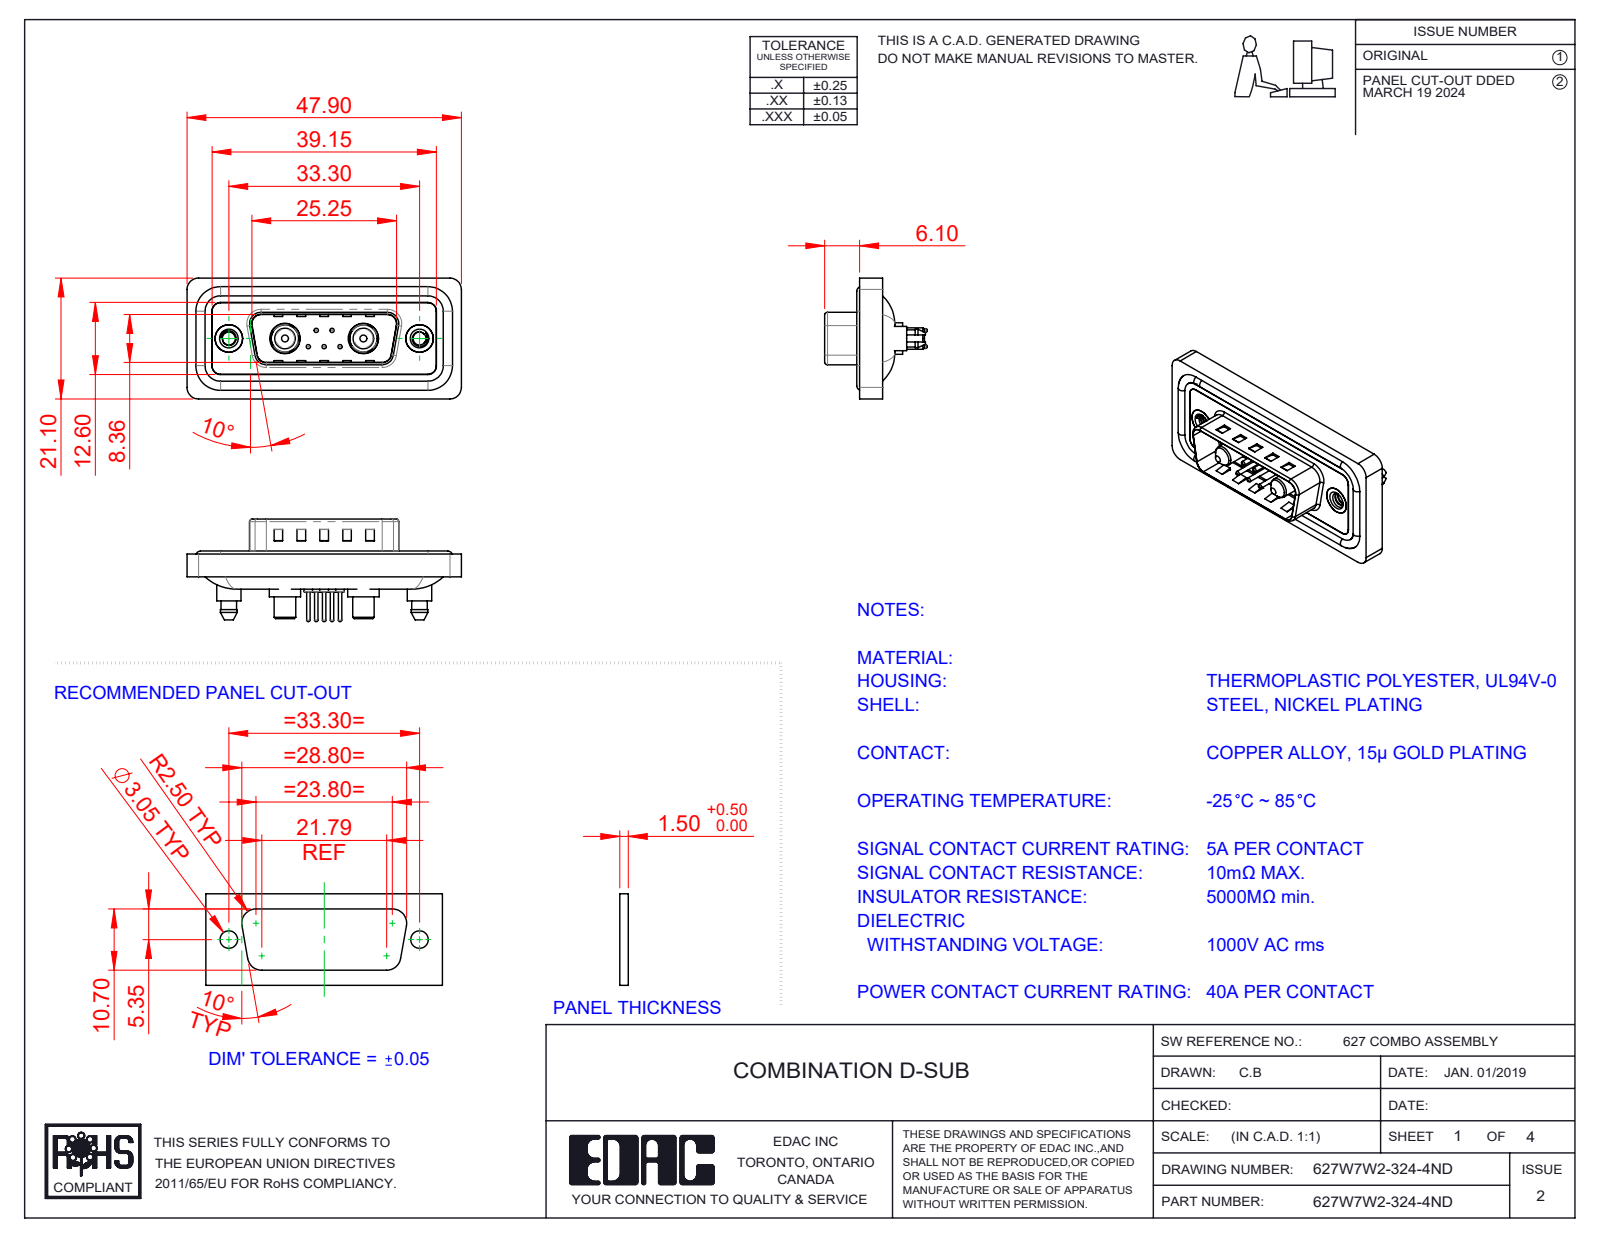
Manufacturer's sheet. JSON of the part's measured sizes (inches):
{"part_name": "627Combo Shell Front_15 Contacts; 627Combo Threaded Boardlock_5; 627Combo Shell Rear_15 Contacts; 627Combo Contact Row 2_24 (+6 more)", "step_written_by": "SolidWorks 2023 (CONFIG_CONTROL_DESIGN)", "units": "inches", "bodies": {"solids": 16, "faces": 768, "planar": 248, "cylindrical": 332, "other": 188}, "overall_size": [1.886, 0.831, 0.705], "volume_in3": 0.347, "surface_area_in2": 14.18, "round_holes": [[0.03, 5], [0.063, 5], [0.079, 5], [0.089, 2], [0.157, 2], [0.189, 2], [0.191, 2], [0.197, 2], [0.209, 2]], "round_bosses_or_shafts": [[0.059, 5], [0.024, 5], [0.063, 4], [0.217, 2], [0.213, 2], [0.205, 2], [0.193, 2], [0.187, 2]], "partial_cylinders_radius": [[0.059, 28], [0.079, 20], [0.063, 10], [0.02, 8], [0.01, 4], [0.024, 4], [0.026, 4], [0.035, 4]], "face_to_face_distances": [0.016, 0.043, 0.063, 0.059, 0.122, 0.02, 0.114, 0.028, 0.032, 0.377], "hole_center_spacings": [0.124, 0.109, 0.386, 0.925, 0.17, 0.17, 0.198, 0.198]}
